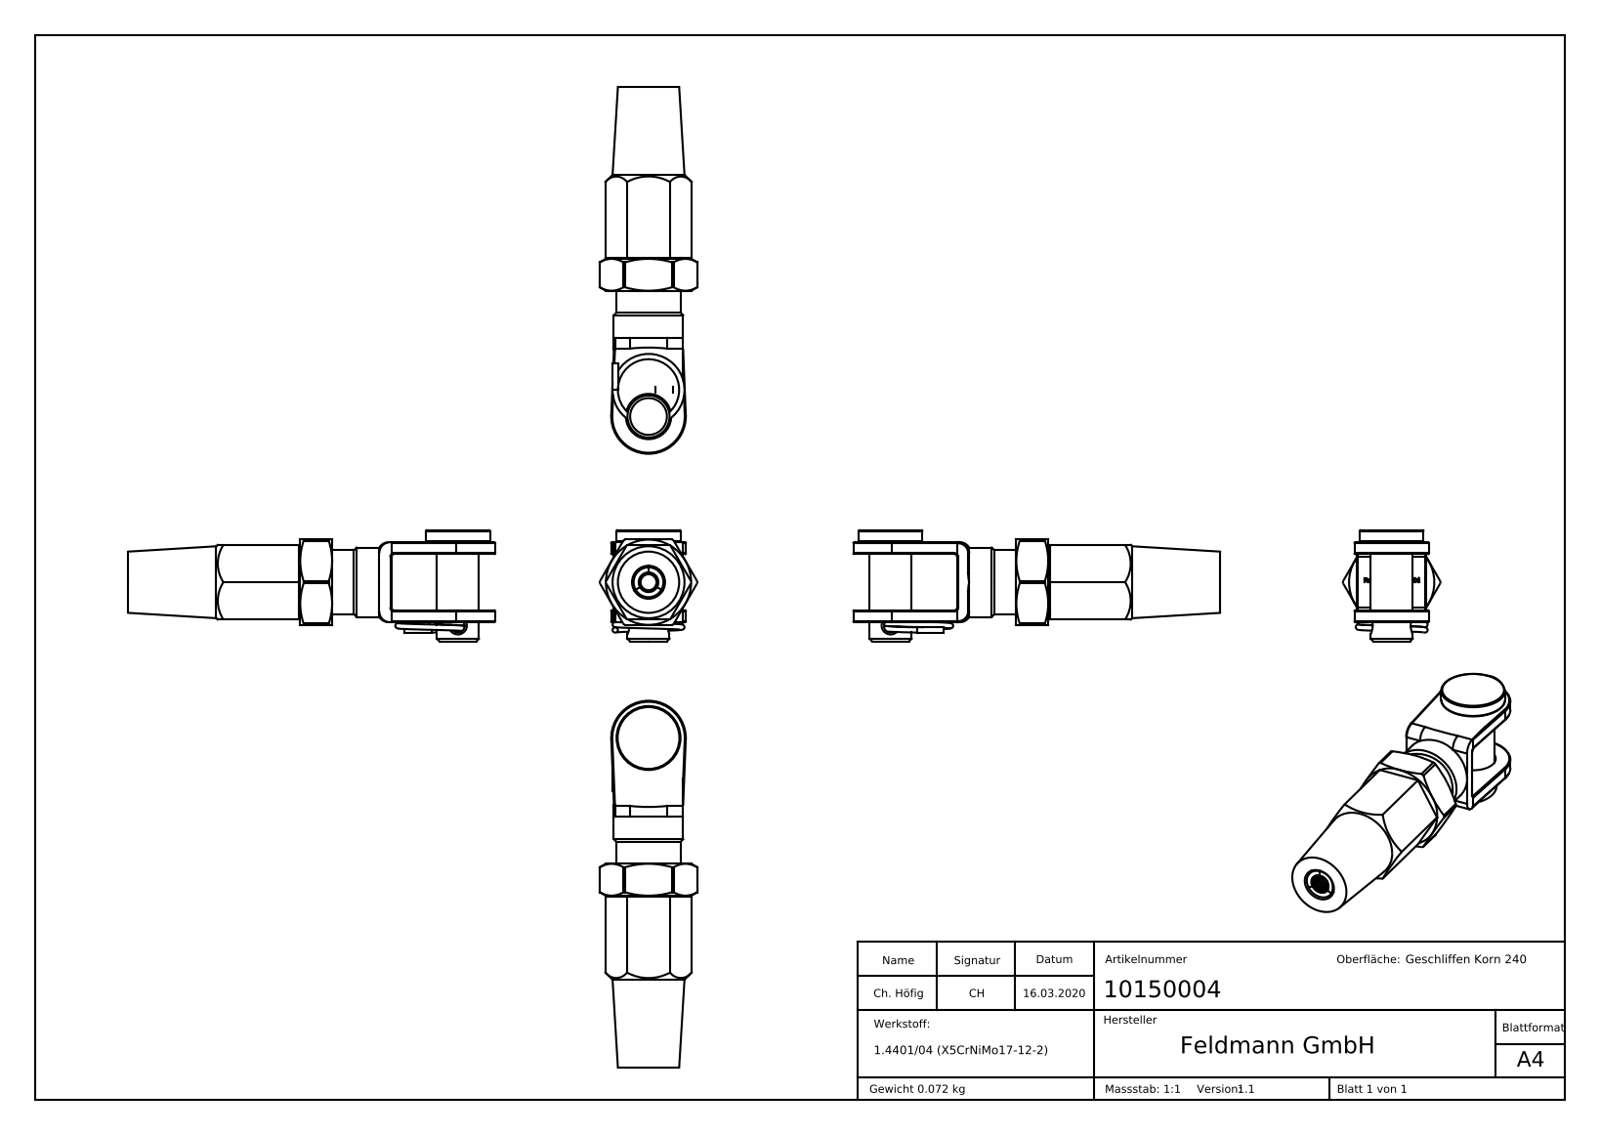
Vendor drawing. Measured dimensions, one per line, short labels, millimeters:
name: 1015000X Teil5_10150004 Teil5; 1015000X Teil4; 1015000X Teil7; 1015000X Teil4_10150004 Teil4 (+8 more)
written by: SolidWorks 2015 (CONFIG_CONTROL_DESIGN)
unit: mm
bodies: 10 solids, 554 faces (161 planar, 142 cylindrical, 251 other)
size: 68.85 × 20.9 × 18.32
volume: 8 970 mm³; area: 7 874 mm²
holes: 1× ⌀2.5, 1× ⌀3.5, 1× ⌀4, 1× ⌀5, 1× ⌀8.5, 1× ⌀8.68, 1× ⌀10.2
bosses: 2× ⌀12, 2× ⌀1, 1× ⌀13, 1× ⌀8, 1× ⌀7.9
rounds: 13× R0.2, 8× R0.5, 2× R2, 1× R7
face distances: 15, 2.25, 14, 12.75, 0.5, 12.25, 1, 14.5, 1.75, 10.5
